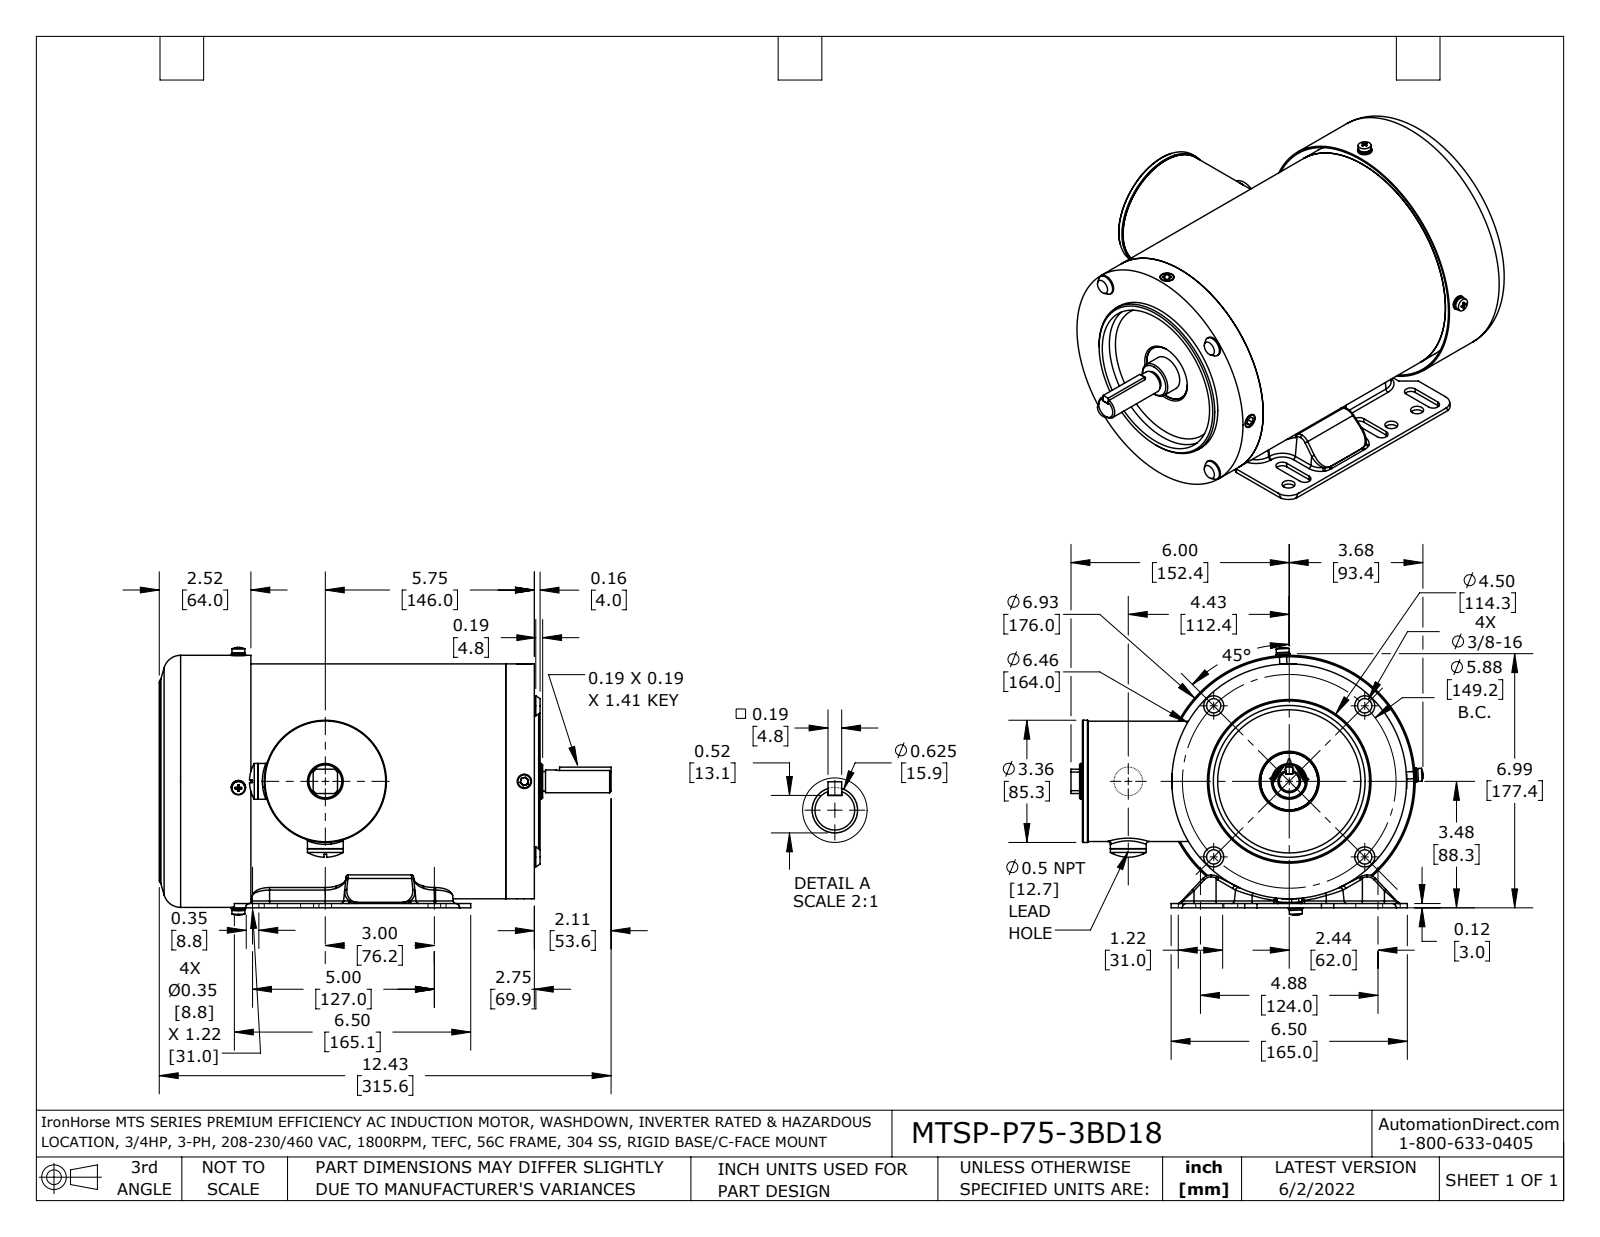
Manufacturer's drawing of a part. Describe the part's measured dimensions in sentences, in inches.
The part is named "MTSP-P75-3BD18". Its 3-D file was written by "SolidWorks 2021 (AUTOMOTIVE_DESIGN)". It is 40 solids with 1658 faces: 444 planar, 582 cylindrical and 632 other. Overall it measures 12.425 by 9.68 by 7.357 inches. Its volume is 58.18 cubic inches and its surface area 996.7 square inches. Round holes: 10 of diameter 0.165, 8 of diameter 0.217, 6 of diameter 0.358, 4 of diameter 0.213, 4 of diameter 0.236, 4 of diameter 0.256, 4 of diameter 0.335, 2 of diameter 0.118, 2 of diameter 0.354, 2 of diameter 0.472, 2 of diameter 0.656, 2 of diameter 1.378. Round bosses or shafts: 6 of diameter 0.394, 4 of diameter 0.551, 4 of diameter 0.354, 4 of diameter 0.331, 4 of diameter 0.315, 4 of diameter 0.197, 3 of diameter 0.984, 2 of diameter 0.787. Partial cylindrical surfaces (rounded edges, fillets, slot ends): 56 of radius 0.079, 39 of radius 0.039, 36 of radius 0.128, 16 of radius 0.012, 14 of radius 0.118, 12 of radius 0.173, 8 of radius 0.236, 6 of radius 0.059. The main face-to-face distances are 0.118, 8.307, 0.236, 0.039, 8.071, 8.189, 8.425, 1.949, 1.831, 10.256. The hole center spacings are 2.937, 4.154, 0.143, 1.181, 1.322, 2.231, 2.311, 2.498.
